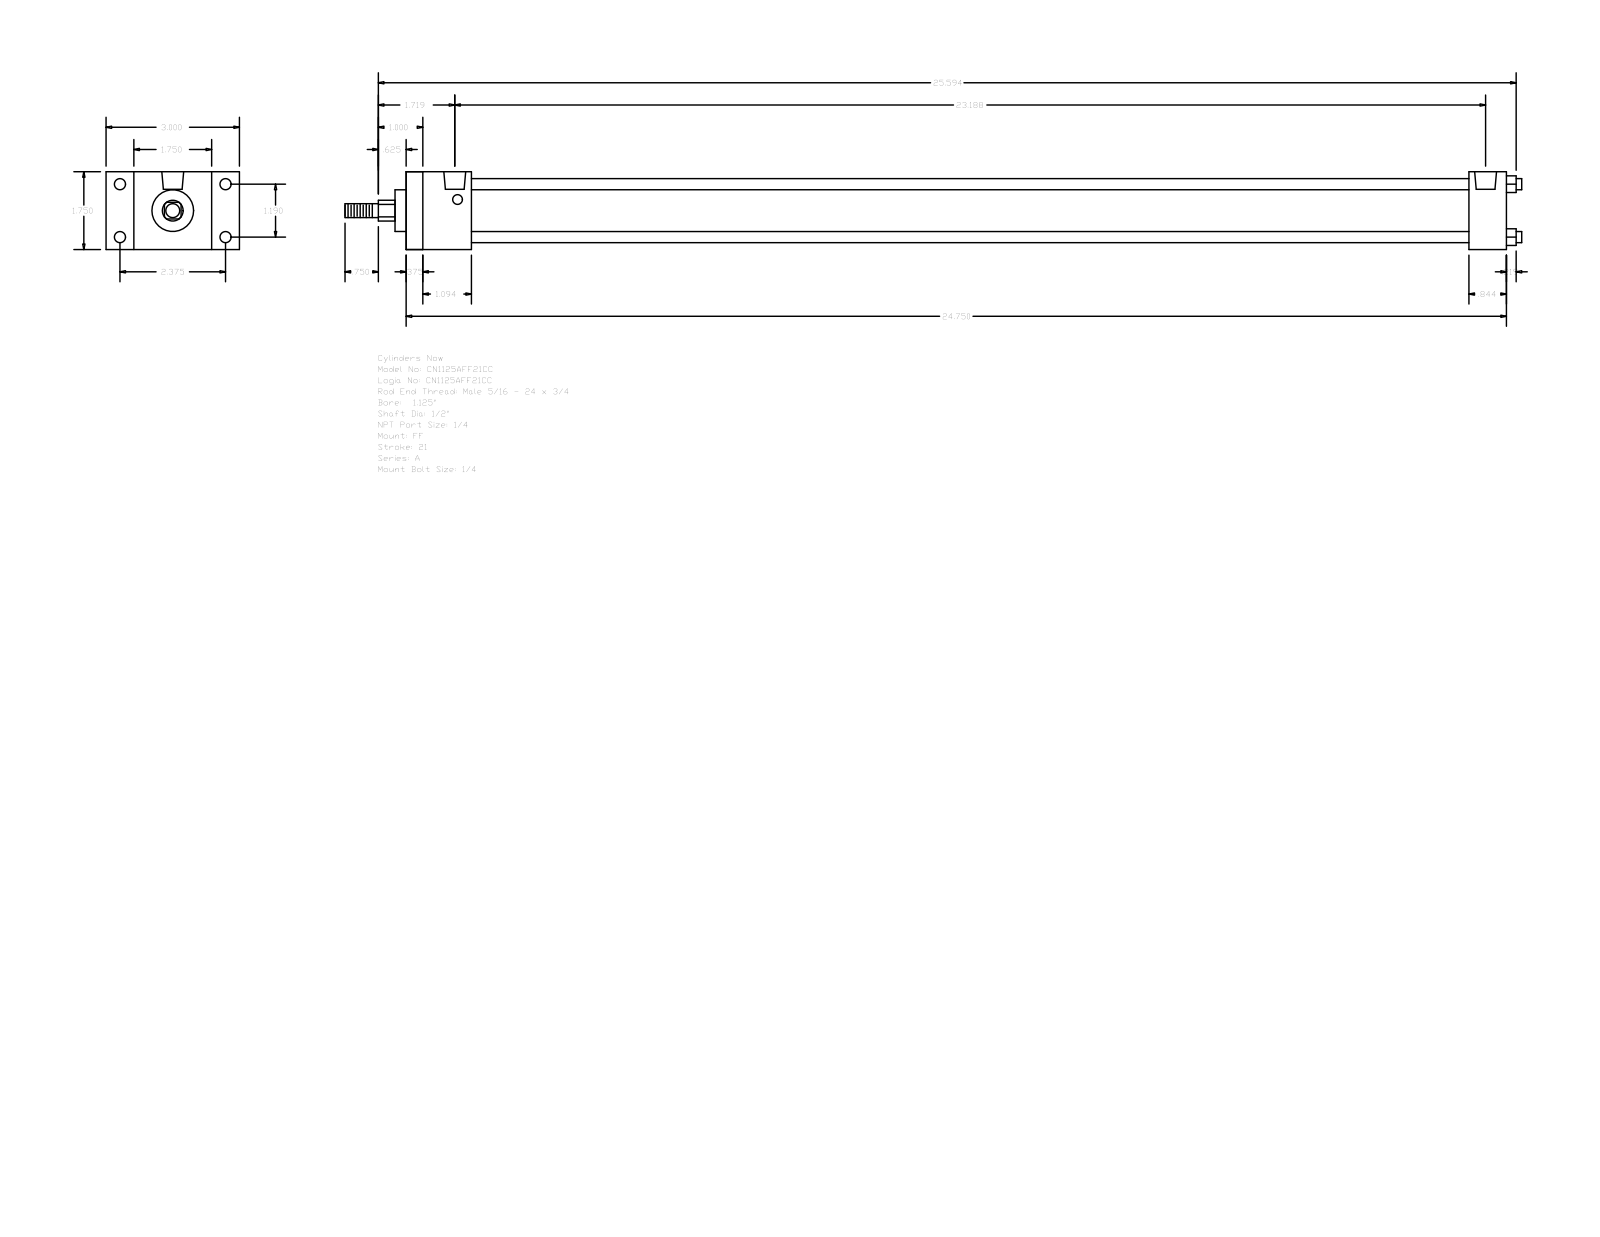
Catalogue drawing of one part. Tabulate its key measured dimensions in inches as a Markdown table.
| quantity | value |
| --- | --- |
| part name | A_FF__0112_0.5 |
| STEP written by | GSSL Pune (CONFIG_CONTROL_DESIGN) |
| units | inches |
| bodies | 0 solids, 92 faces (64 planar, 28 cylindrical, 0 other) |
| overall size | 26.469 × 3 × 1.75 |
| round holes (diameter × count) | 0.219 × 4, 0.25 × 4, 0.492 × 2 |
| round bosses / shafts (diameter × count) | 0.25 × 4, 1.255 × 1, 0.937 × 1, 0.5 × 1, 0.313 × 1 |
| partial cylindrical surfaces (radius × count) | 0.234 × 1 |
| main face-to-face distances | 1.75, 24.75, 0.375, 24.375, 0.625, 23.906, 23.531, 0.844, 1.469, 1.094 |
| hole center spacings | 1.19, 2.375, 2.656, 23.063, 0.062, 0.063, 23.125, 23.125 |
